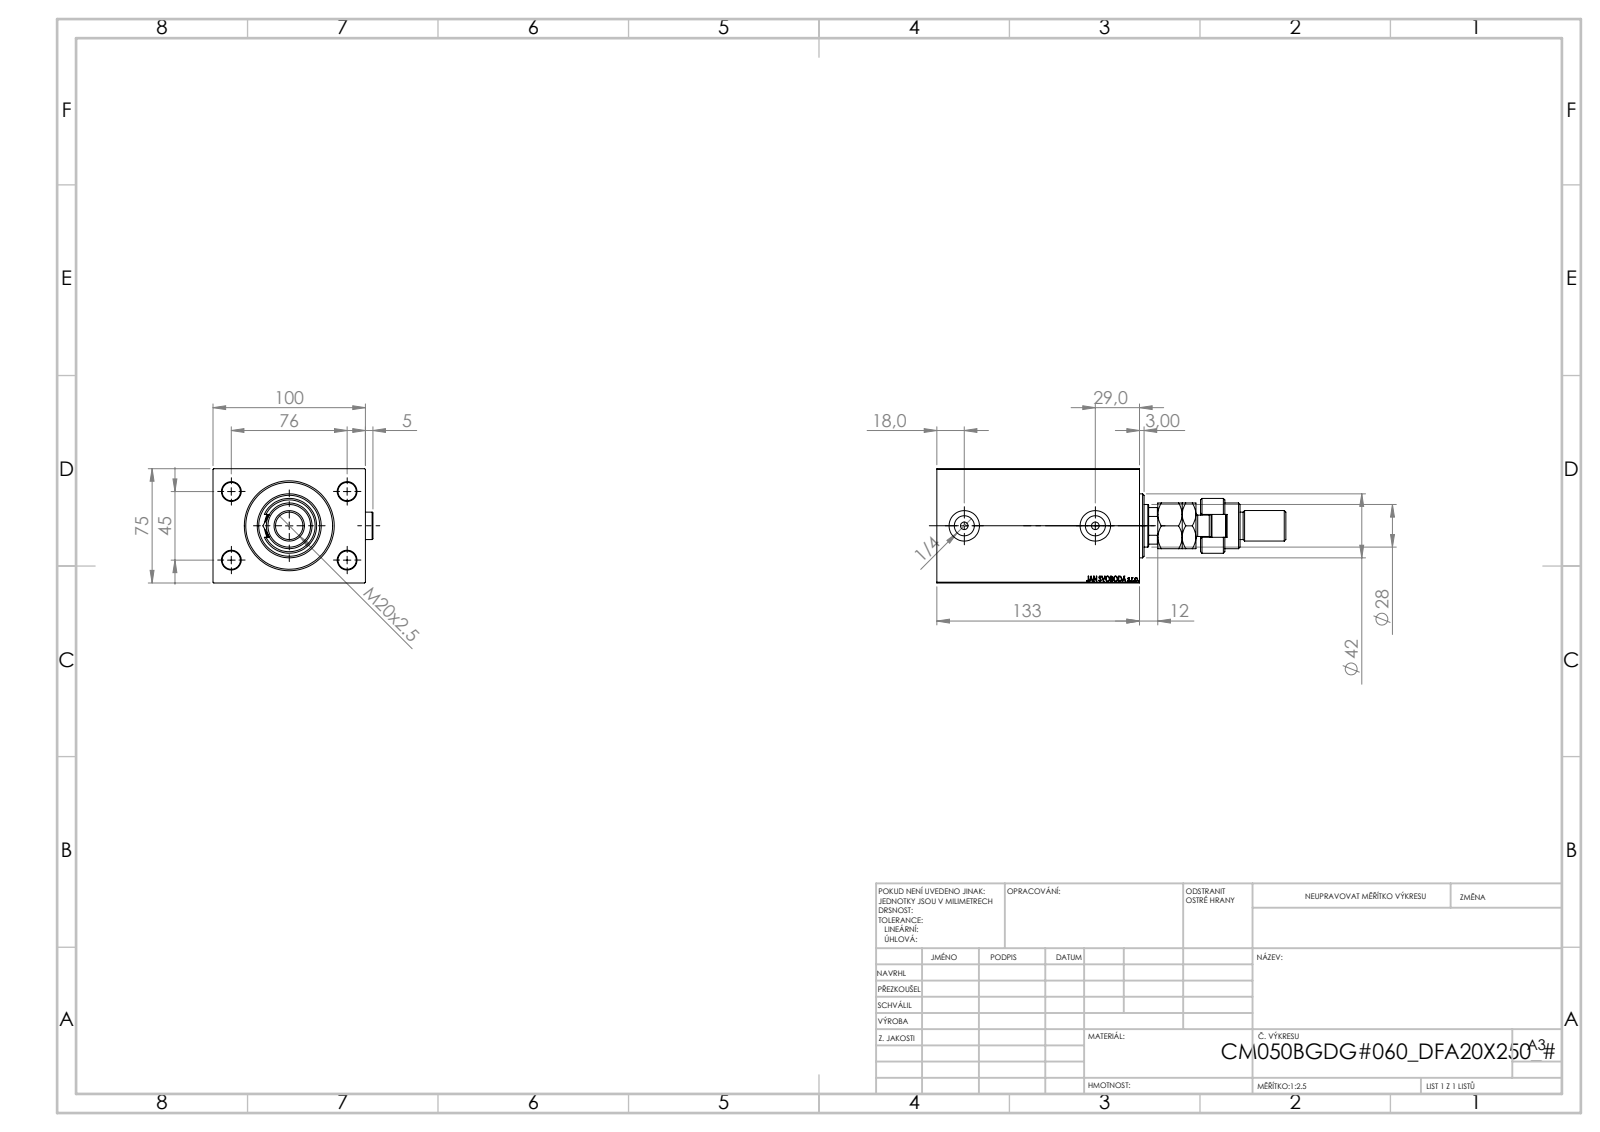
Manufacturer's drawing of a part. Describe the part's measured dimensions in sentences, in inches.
The part is named "V450CM_B_VCP; MFA; V450CM_B_Body; V450CM_VC_B (+2 more)". Its 3-D file was written by "SolidWorks 2019 (CONFIG_CONTROL_DESIGN)". It is 7 solids with 1023 faces: 464 planar, 85 cylindrical and 474 other. Overall it measures 9.016 by 4.13 by 2.953 inches. Its volume is 57.48 cubic inches and its surface area 204.2 square inches. Round holes: 4 of diameter 0.472, 2 of diameter 0.197, 2 of diameter 0.518, 2 of diameter 0.787, 1 of diameter 0.728, 1 of diameter 1.102, 1 of diameter 1.24, 1 of diameter 1.28, 1 of diameter 1.969, 1 of diameter 2.047, 1 of diameter 2.244. Round bosses or shafts: 3 of diameter 0.709, 1 of diameter 1.654, 1 of diameter 1.417, 1 of diameter 1.181, 1 of diameter 0.866, 1 of diameter 0.787, 1 of diameter 0.551. Partial cylindrical surfaces (rounded edges, fillets, slot ends): 1 of radius 0.295, 1 of radius 0.472, 1 of radius 0.531. The main face-to-face distances are 2.953, 3.937, 5.236, 4.685, 0.551, 0.472, 1.181, 4.764, 4.213, 1.85. The hole center spacings are 1.739, 1.772, 2.992, 3.477, 3.386.
